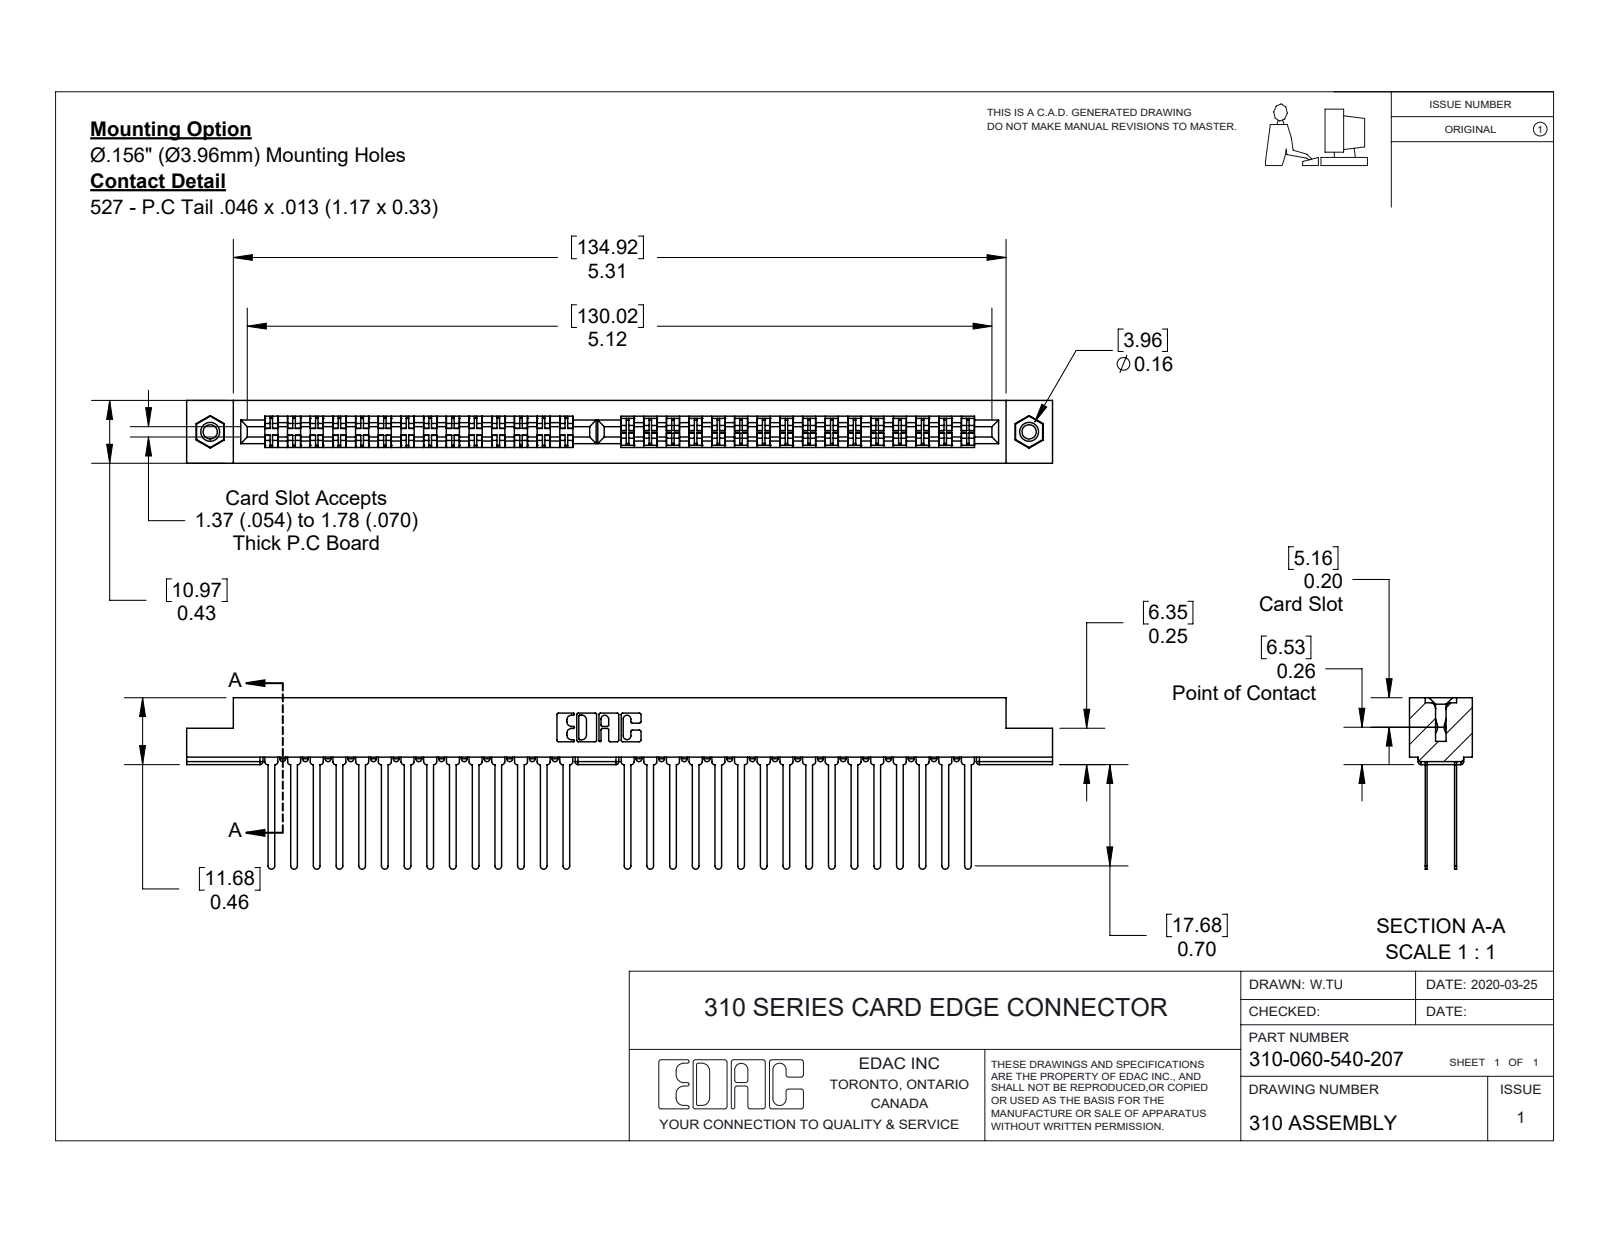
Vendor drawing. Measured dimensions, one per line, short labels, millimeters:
name: 310 Part_.116 Hex; 310-060-540-207; 345-250-001_345-250-005-103; 307-290-001_540
written by: SolidWorks 2016 (CONFIG_CONTROL_DESIGN)
unit: mm
bodies: 63 solids, 2986 faces (1976 planar, 930 cylindrical, 80 other)
size: 151.21 × 29.95 × 10.97
volume: 13 332 mm³; area: 20 207 mm²
holes: 2× ⌀2.5, 2× ⌀3.17, 2× ⌀3.96
bosses: 2× ⌀3.94
rounds: 158× R0.51, 30× R0.58, 22× R0.25, 6× R0.17, 6× R0.8, 4× R0.3, 4× R0.64, 4× R1.19
face distances: 0.33, 2.76, 0.38, 8.22, 4.75, 5.08, 3.14, 7.84, 10.98, 3.47
hole spacings: 143
